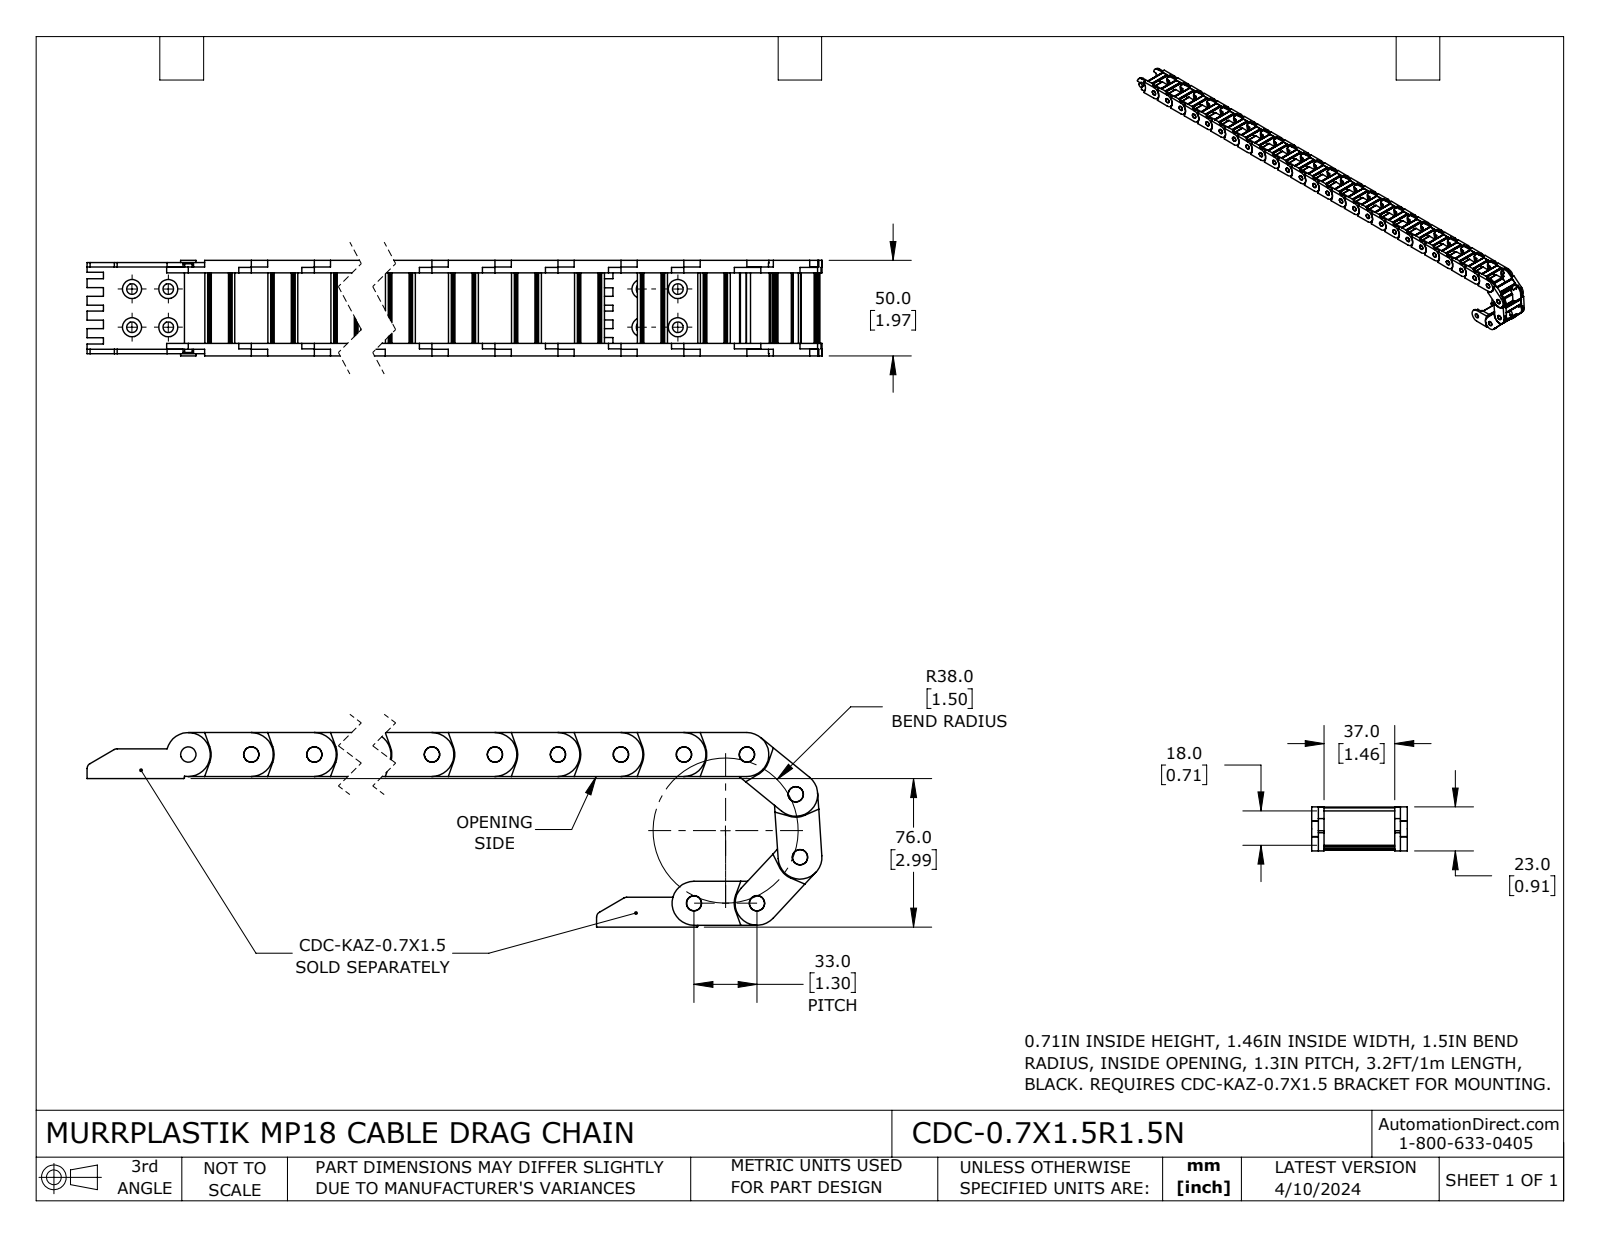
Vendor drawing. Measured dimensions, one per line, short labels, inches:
name: CDC-0.7X1.5R1.5N
written by: SolidWorks 2023 (CONFIG_CONTROL_DESIGN)
unit: in
bodies: 30 solids, 2370 faces (1110 planar, 1260 cylindrical, 0 other)
size: 35.773 × 3.972 × 1.969
volume: 19.75 in³; area: 377.9 in²
holes: 30× ⌀0.315
bosses: 1× ⌀0.315
rounds: 120× R0.02, 120× R0.059, 60× R0.008, 60× R0.012, 31× R0.453, 31× R0.47, 30× R0.197, 30× R0.215
face distances: 1.713, 0.256, 1.969, 0.138, 1.831, 0.118, 1.575, 0.146, 1.823, 1.685
hole spacings: 1.299, 2.598, 3.898, 5.197, 6.496, 7.795, 9.094, 10.394
